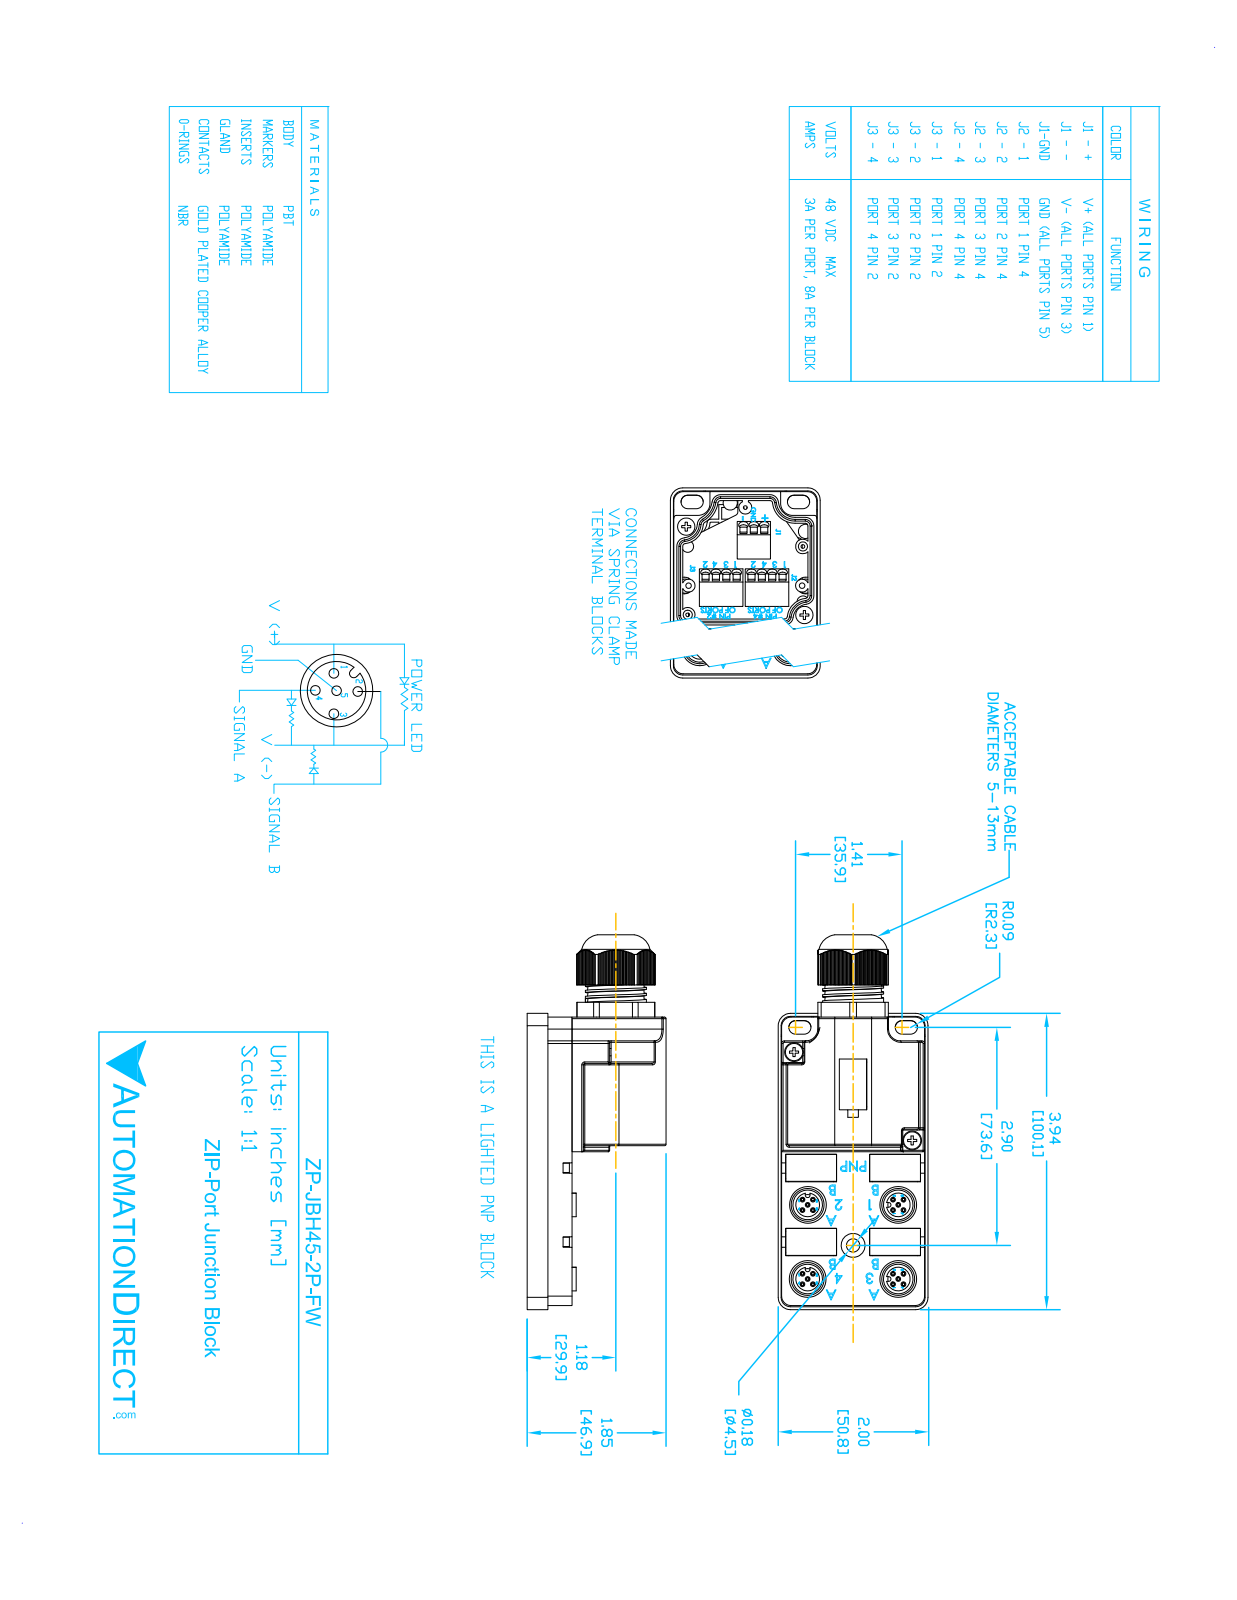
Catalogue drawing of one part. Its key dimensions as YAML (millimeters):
part_name: "ZP-JBH45-00-FW"
step_written_by: "SolidWorks 2016 (AUTOMOTIVE_DESIGN)"
units: millimeters
bodies: {solids: 7, faces: 1065, planar: 636, cylindrical: 267, other: 162}
overall_size: [126.62, 50.57, 46.89]
volume: 131541
surface_area: 29065
round_holes:
  - {diameter: 1.09, count: 20}
  - {diameter: 1.6, count: 20}
  - {diameter: 11.1, count: 4}
  - {diameter: 12.4, count: 4}
  - {diameter: 6.35, count: 2}
  - {diameter: 6.6, count: 1}
  - {diameter: 8.08, count: 1}
  - {diameter: 9.4, count: 1}
  - {diameter: 12.45, count: 1}
  - {diameter: 15.16, count: 1}
round_bosses_or_shafts:
  - {diameter: 8, count: 3}
  - {diameter: 20.57, count: 1}
  - {diameter: 20, count: 1}
  - {diameter: 8, count: 1}
partial_cylinders:
  - {radius: 0.51, count: 34}
  - {radius: 2.29, count: 8}
  - {radius: 0.8, count: 4}
  - {radius: 4.17, count: 4}
  - {radius: 7.9, count: 4}
  - {radius: 0.89, count: 2}
  - {radius: 3.2, count: 2}
  - {radius: 3.97, count: 2}
face_to_face_distances: [15.14, 43.44, 48.26, 1, 0.89, 14.14, 3.19, 47.38, 1.16, 49.42]
hole_center_spacings: [2.5, 3.54, 30.57, 23.34, 28.85, 30.77, 32.39, 25.04]
